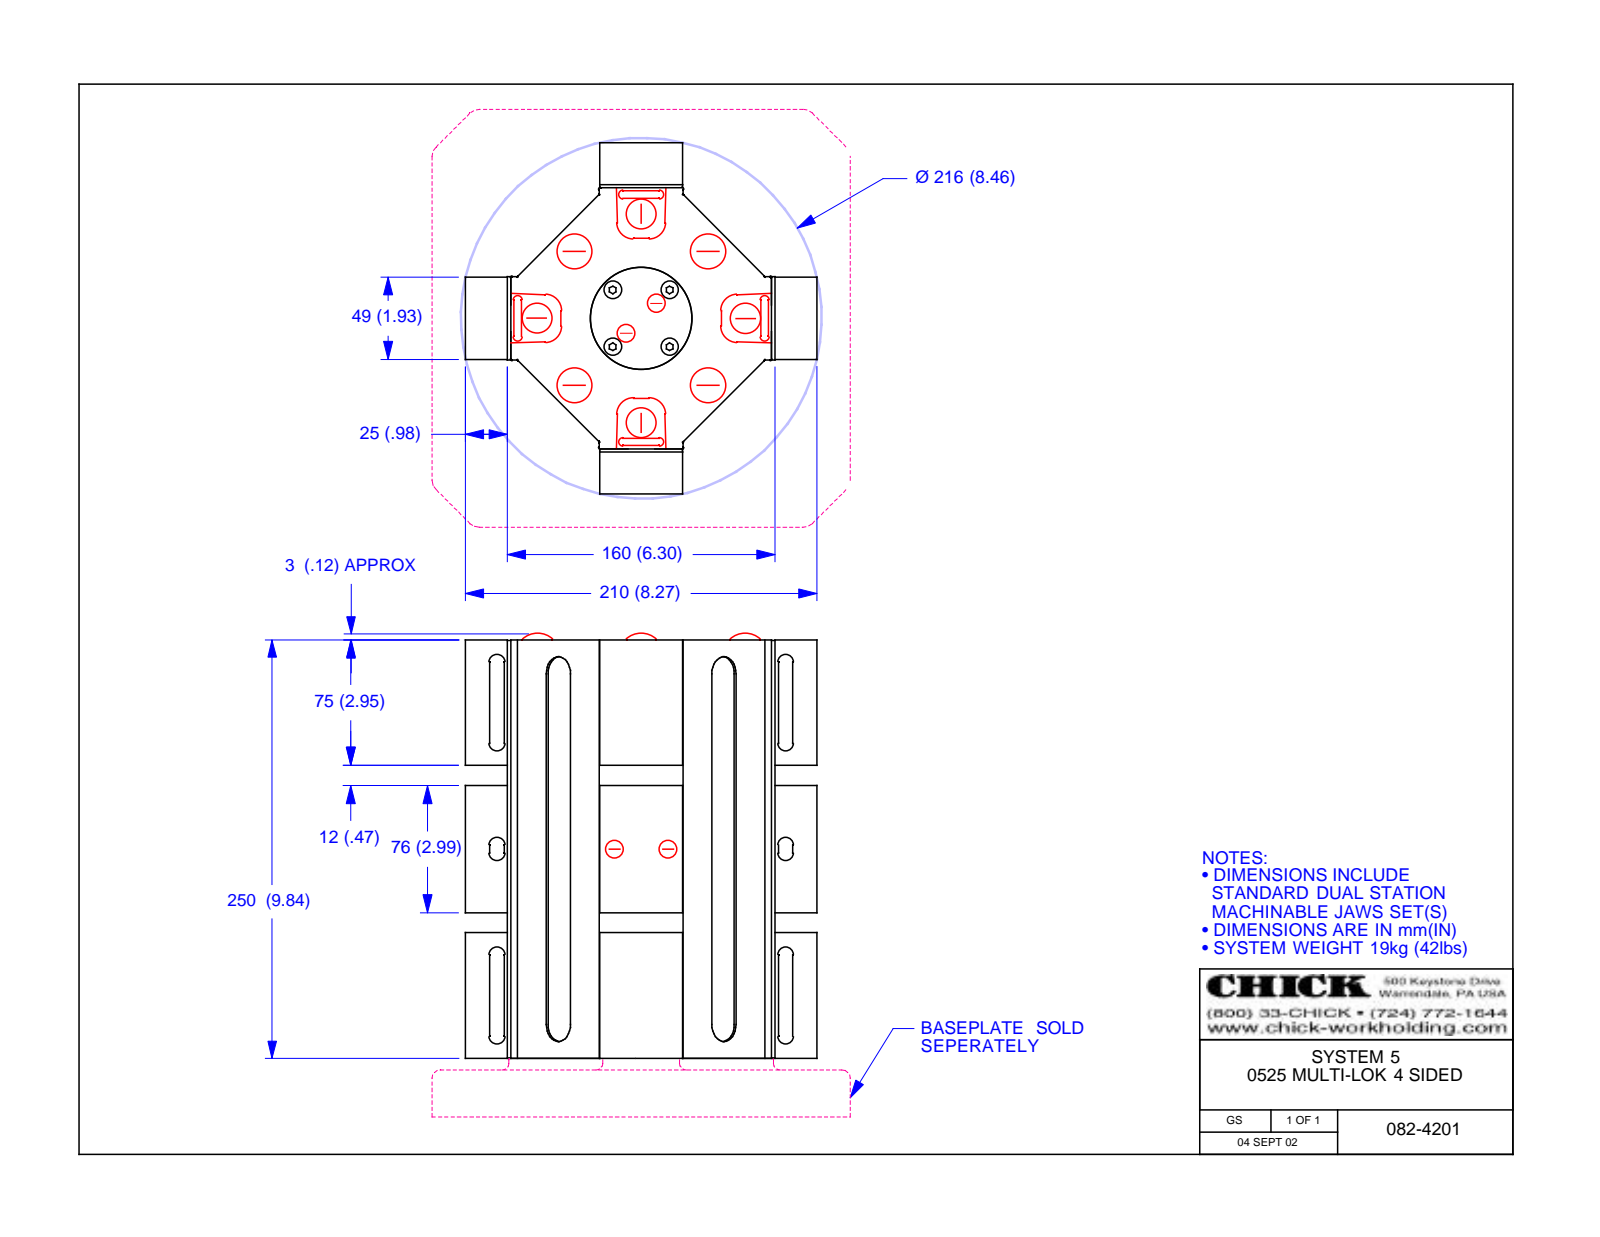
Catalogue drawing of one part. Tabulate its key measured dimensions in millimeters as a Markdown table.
| quantity | value |
| --- | --- |
| part name | 082-4201; 082-4211; 5CP0525-ST; 080-2505 (+2 more) |
| STEP written by | Autodesk Inventor 2013 (AUTOMOTIVE_DESIGN) |
| units | millimeters |
| bodies | 41 solids, 2582 faces (1198 planar, 516 cylindrical, 868 other) |
| overall size | 254 × 210 × 210 |
| volume | 5 043 000 mm³ |
| surface area | 516 101 mm² |
| round holes (diameter × count) | 10 × 14, 12.7 × 12, 10.11 × 8, 4.06 × 4, 5.2 × 4, 6.87 × 4, 9.14 × 4, 9.65 × 4, 20 × 4, 49.9 × 1, 59.98 × 1 |
| round bosses / shafts (diameter × count) | 14 × 12, 10 × 4, 7.67 × 4, 4.76 × 4 |
| partial cylindrical surfaces (radius × count) | 0.8 × 104, 0.4 × 16, 1 × 16, 1.2 × 16, 0.9 × 8, 1.1 × 8, 1.65 × 8, 1.9 × 8 |
| main face-to-face distances | 158, 2, 72.99, 87.01, 70.99, 85.01, 25, 27, 97.99, 112.01 |
| hole center spacings | 100, 1.22, 18.03, 55.9, 65.76, 79.06, 91.24, 105 |
